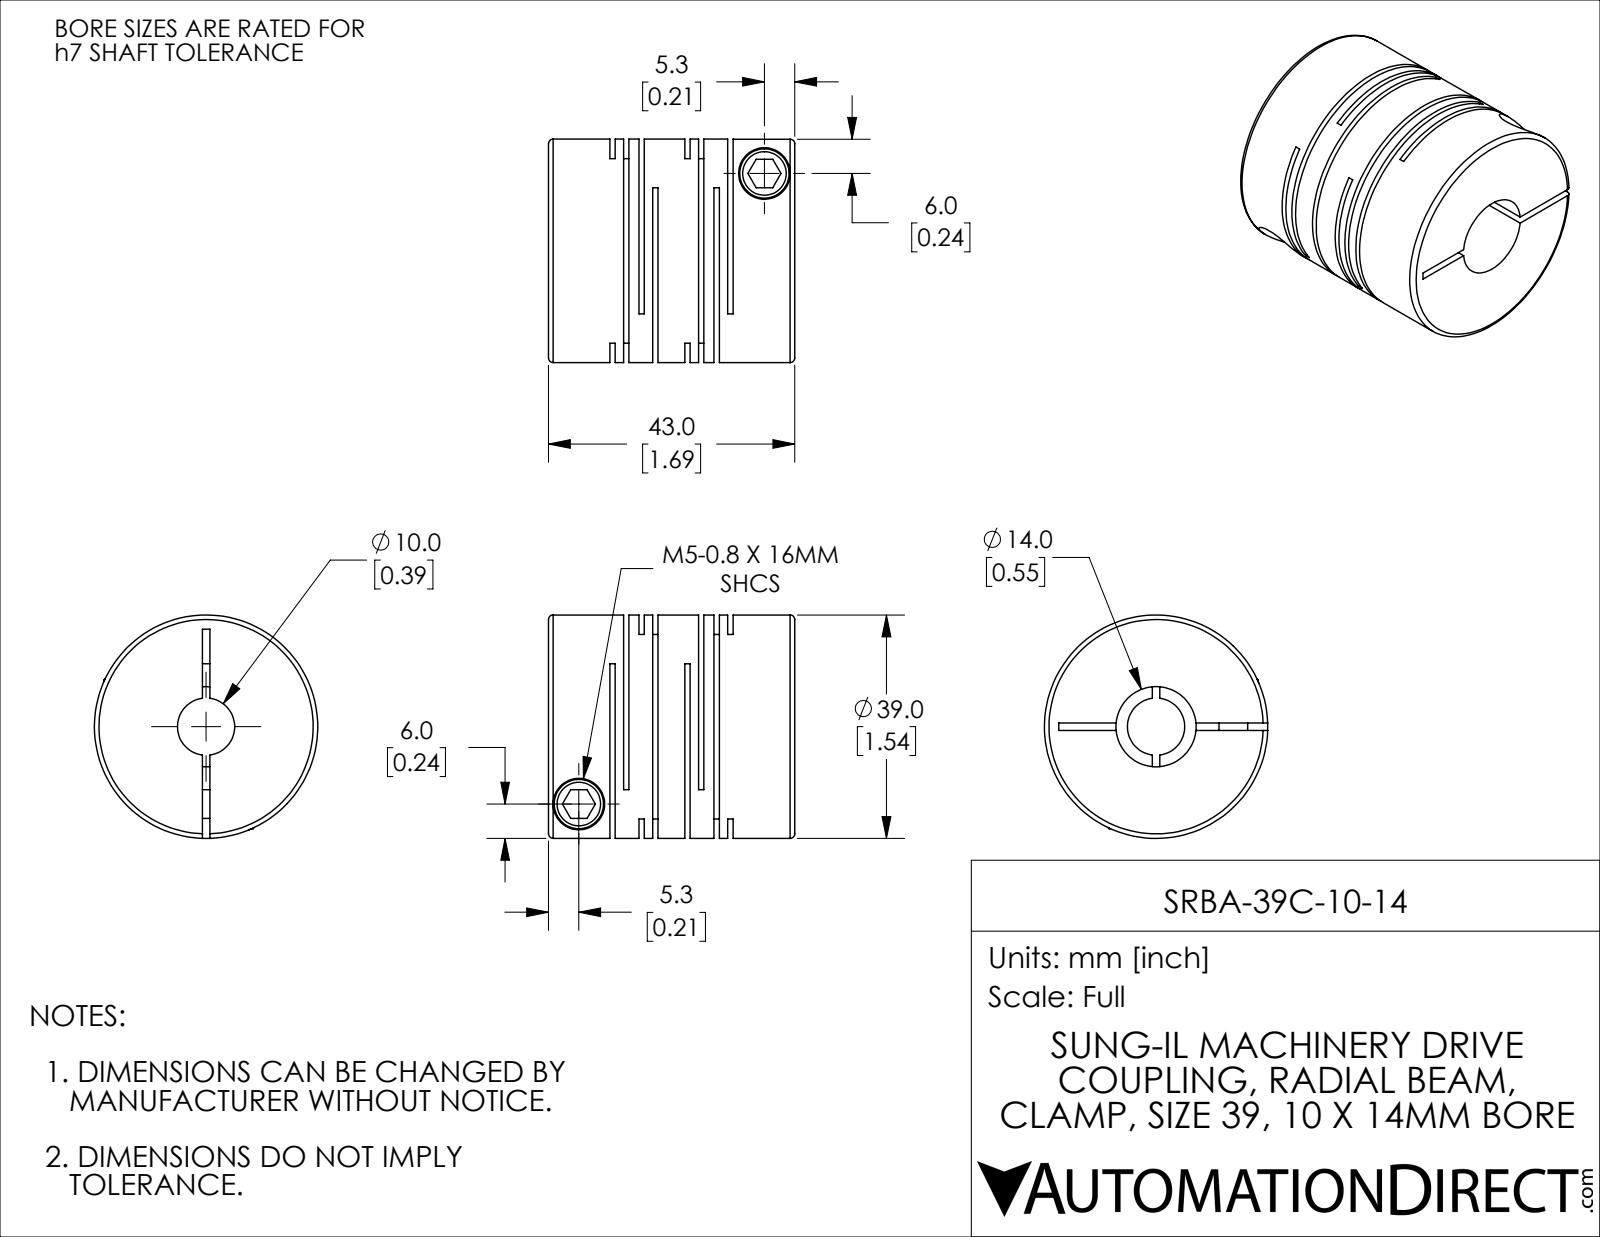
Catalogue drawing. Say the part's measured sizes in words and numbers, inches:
The part is named "SRBA-39C-10-14". Its 3-D file was written by "SolidWorks 2021 (CONFIG_CONTROL_DESIGN)". It is 1 solid with 114 faces: 60 planar, 42 cylindrical and 12 other. Overall it measures 1.693 by 1.535 by 1.535 inches. Its volume is 2.302 cubic inches and its surface area 36.8 square inches. Round holes: 2 of diameter 0.197, 2 of diameter 0.354, 1 of diameter 0.394, 1 of diameter 0.551. Round bosses or shafts: 2 of diameter 0.339, 1 of diameter 1.535. The main face-to-face distances are 0.516, 0.036, 0.094, 0.201, 0.421, 0.552, 0.717, 0.131, 0.61, 0.058.
